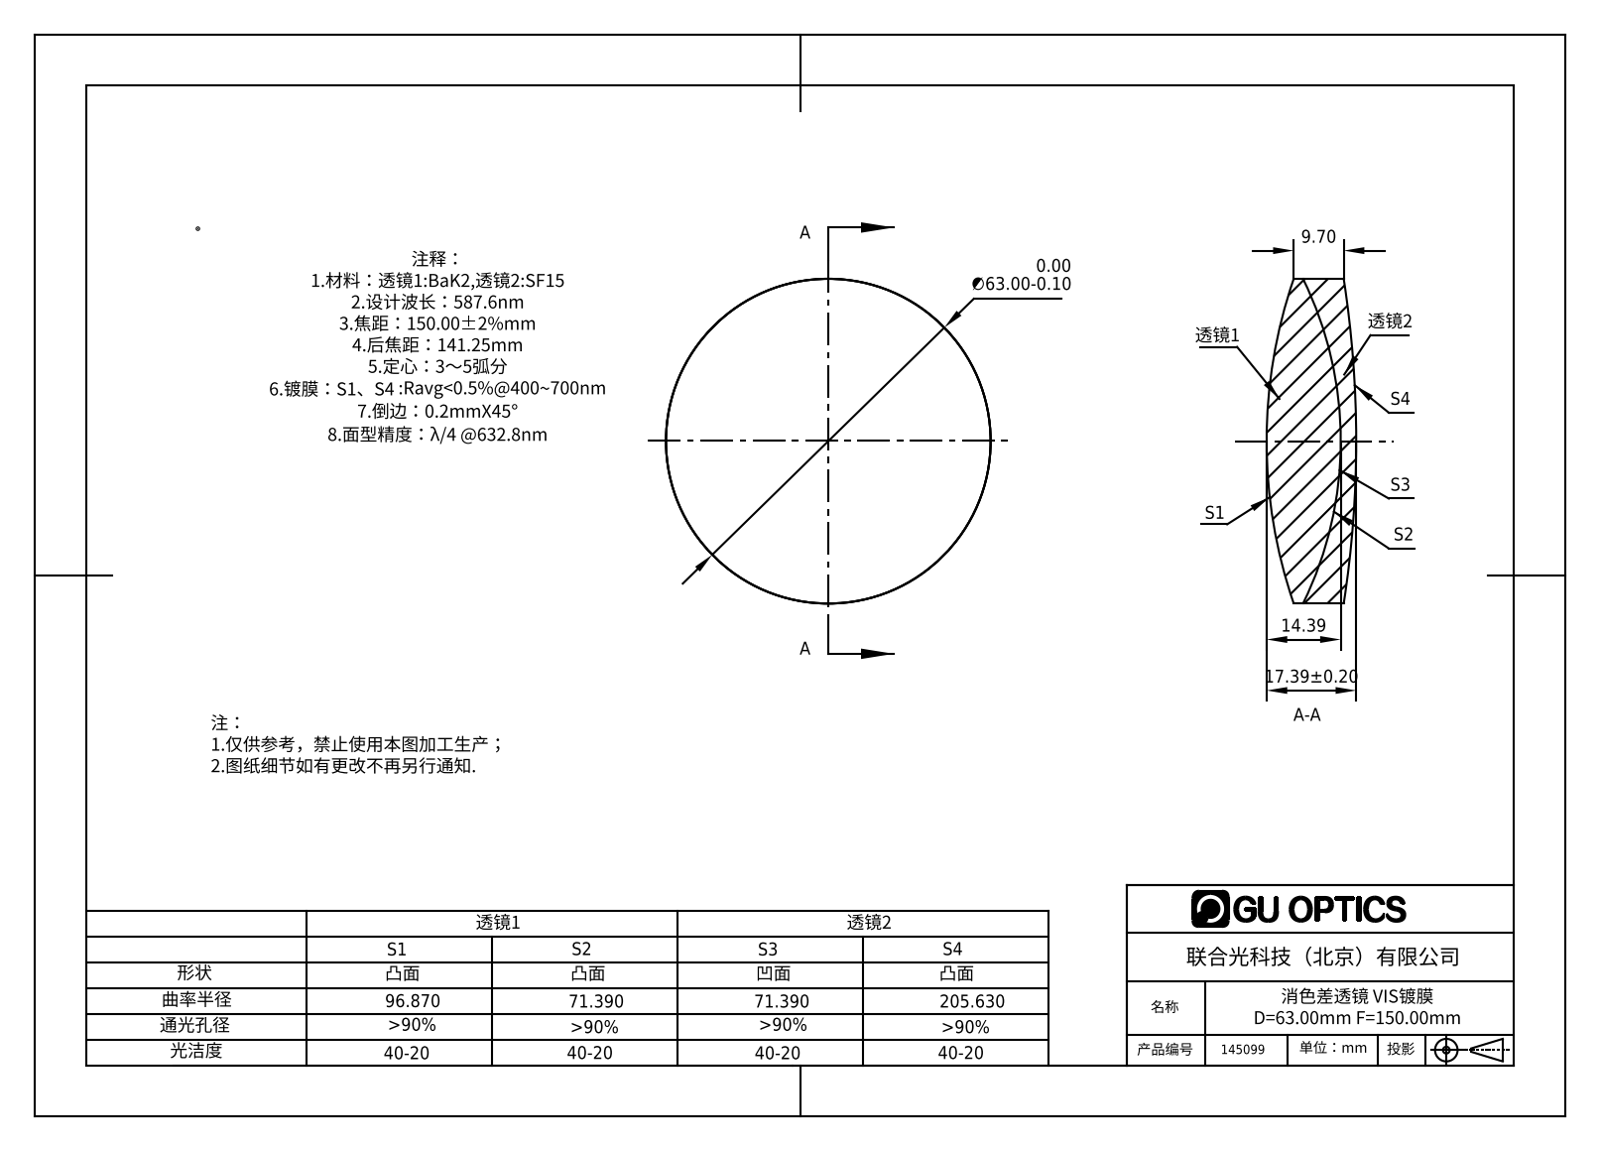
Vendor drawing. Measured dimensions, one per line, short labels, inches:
name: 145099
written by: SolidWorks 2016 (AUTOMOTIVE_DESIGN)
unit: in
bodies: 2 solids, 12 faces (0 planar, 4 cylindrical, 8 other)
size: 2.48 × 2.48 × 0.685
volume: 2.582 in³; area: 22.99 in²
bosses: 1× ⌀2.48
